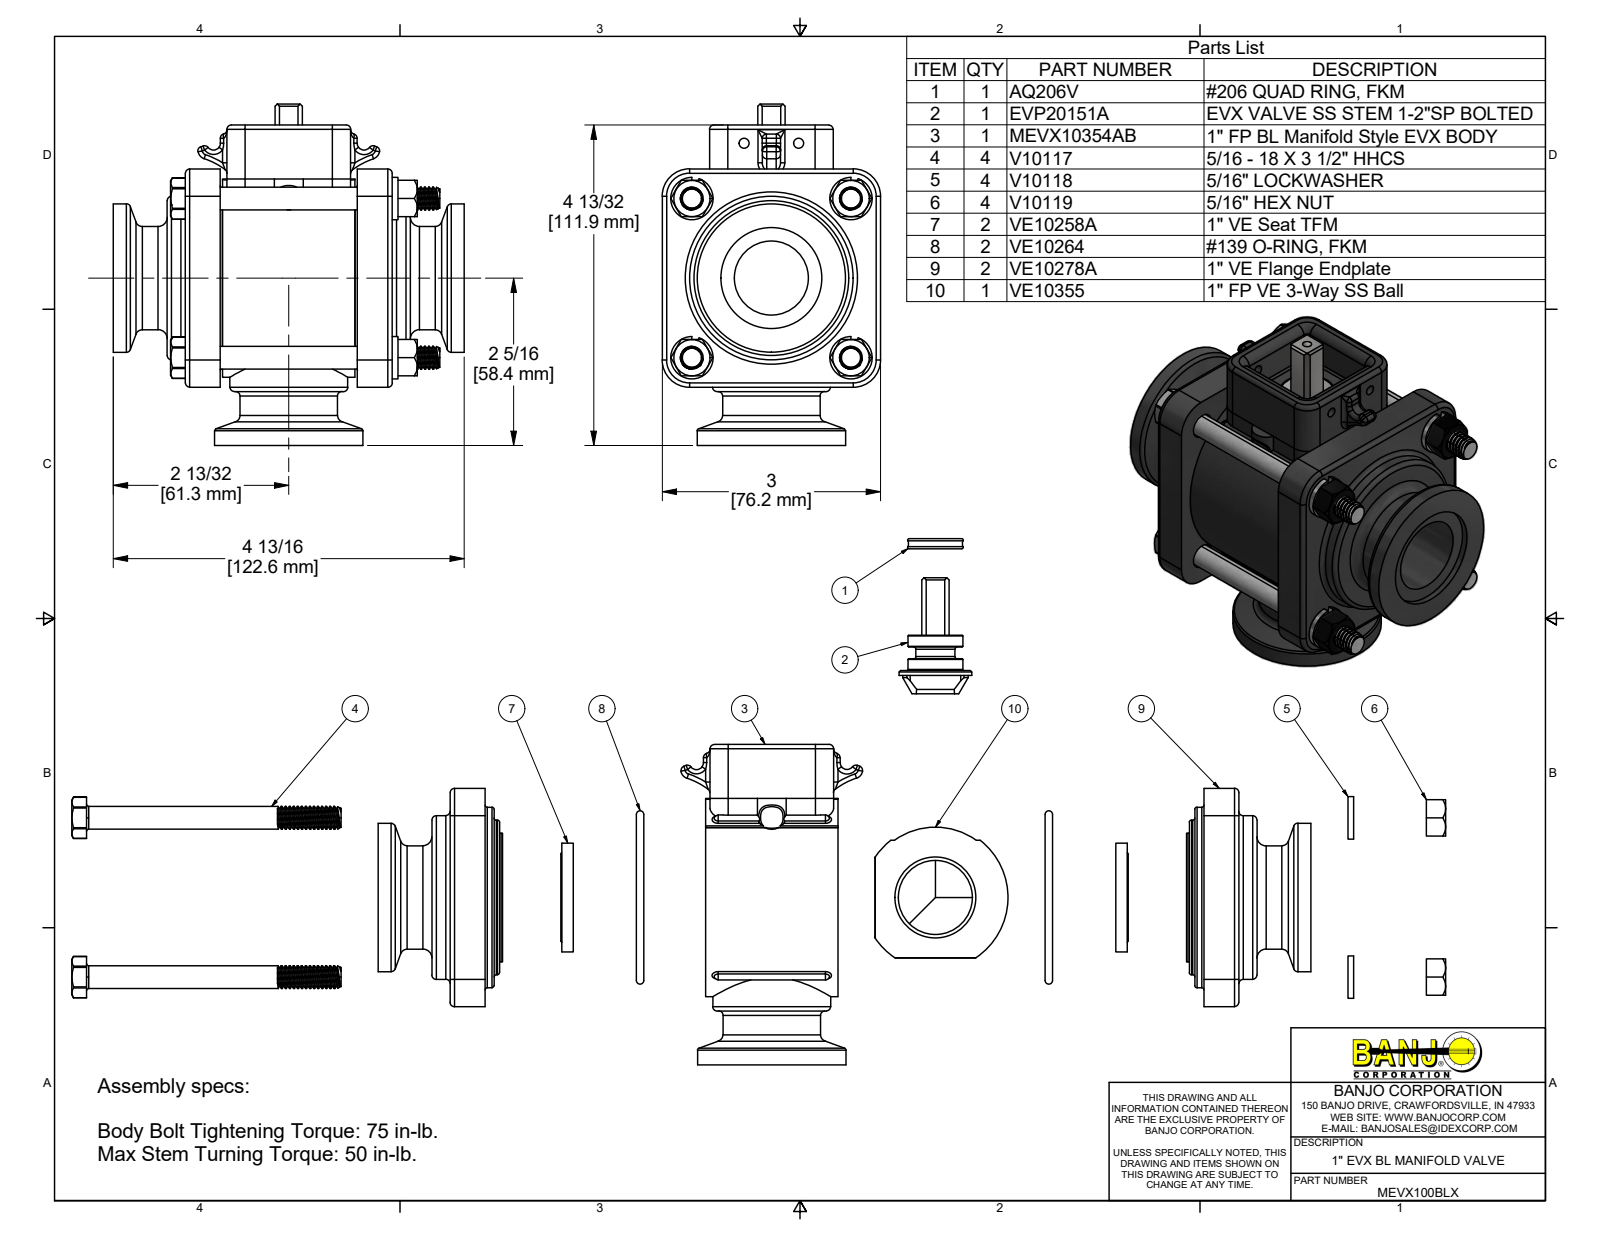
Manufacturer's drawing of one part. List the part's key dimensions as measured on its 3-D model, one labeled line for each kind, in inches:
Part name (STEP PRODUCT): MEVX100BLX; MEVX10354AB; MEVX10354ABX; VE10355 (+8 more)
STEP written by: Autodesk Inventor 2019 (AUTOMOTIVE_DESIGN)
Units: inches
Bodies: 22 solids, 1325 faces (222 planar, 528 cylindrical, 575 other)
Overall size (bounding box): 4.825 × 4.693 × 3
Volume: 22.3 in³ · Surface area: 192.9 in²
Round holes (diameter × count): ⌀0.252 ×4, ⌀0.322 ×4, ⌀0.35 ×4, ⌀1.02 ×3, ⌀0.135 ×2, ⌀0.76 ×1, ⌀1.38 ×1, ⌀1.39 ×1, ⌀1.5 ×1, ⌀2.12 ×1, ⌀2.375 ×1, ⌀2.5 ×1
Round bosses / shafts (diameter × count): ⌀0.268 ×60, ⌀0.583 ×4, ⌀0.313 ×4, ⌀2.04 ×2, ⌀2.725 ×1, ⌀2.48 ×1, ⌀2.25 ×1, ⌀2.124 ×1
Partial cylindrical surfaces — rounded edges, fillets, slot ends (radius × count): R0.06 ×42, R0.03 ×12, R0.062 ×8, R0.134 ×8, R0.375 ×8, R0.125 ×6, R0.21 ×4, R0.25 ×4
Main face-to-face distances: 0.48, 2.365, 2.845, 3, 0.99, 1.47, 3.355, 3.835, 1.885, 0.605
Hole centre spacings: 1.547, 2.188, 1.891, 3.094, 3.294, 0.75, 1.046, 1.046
